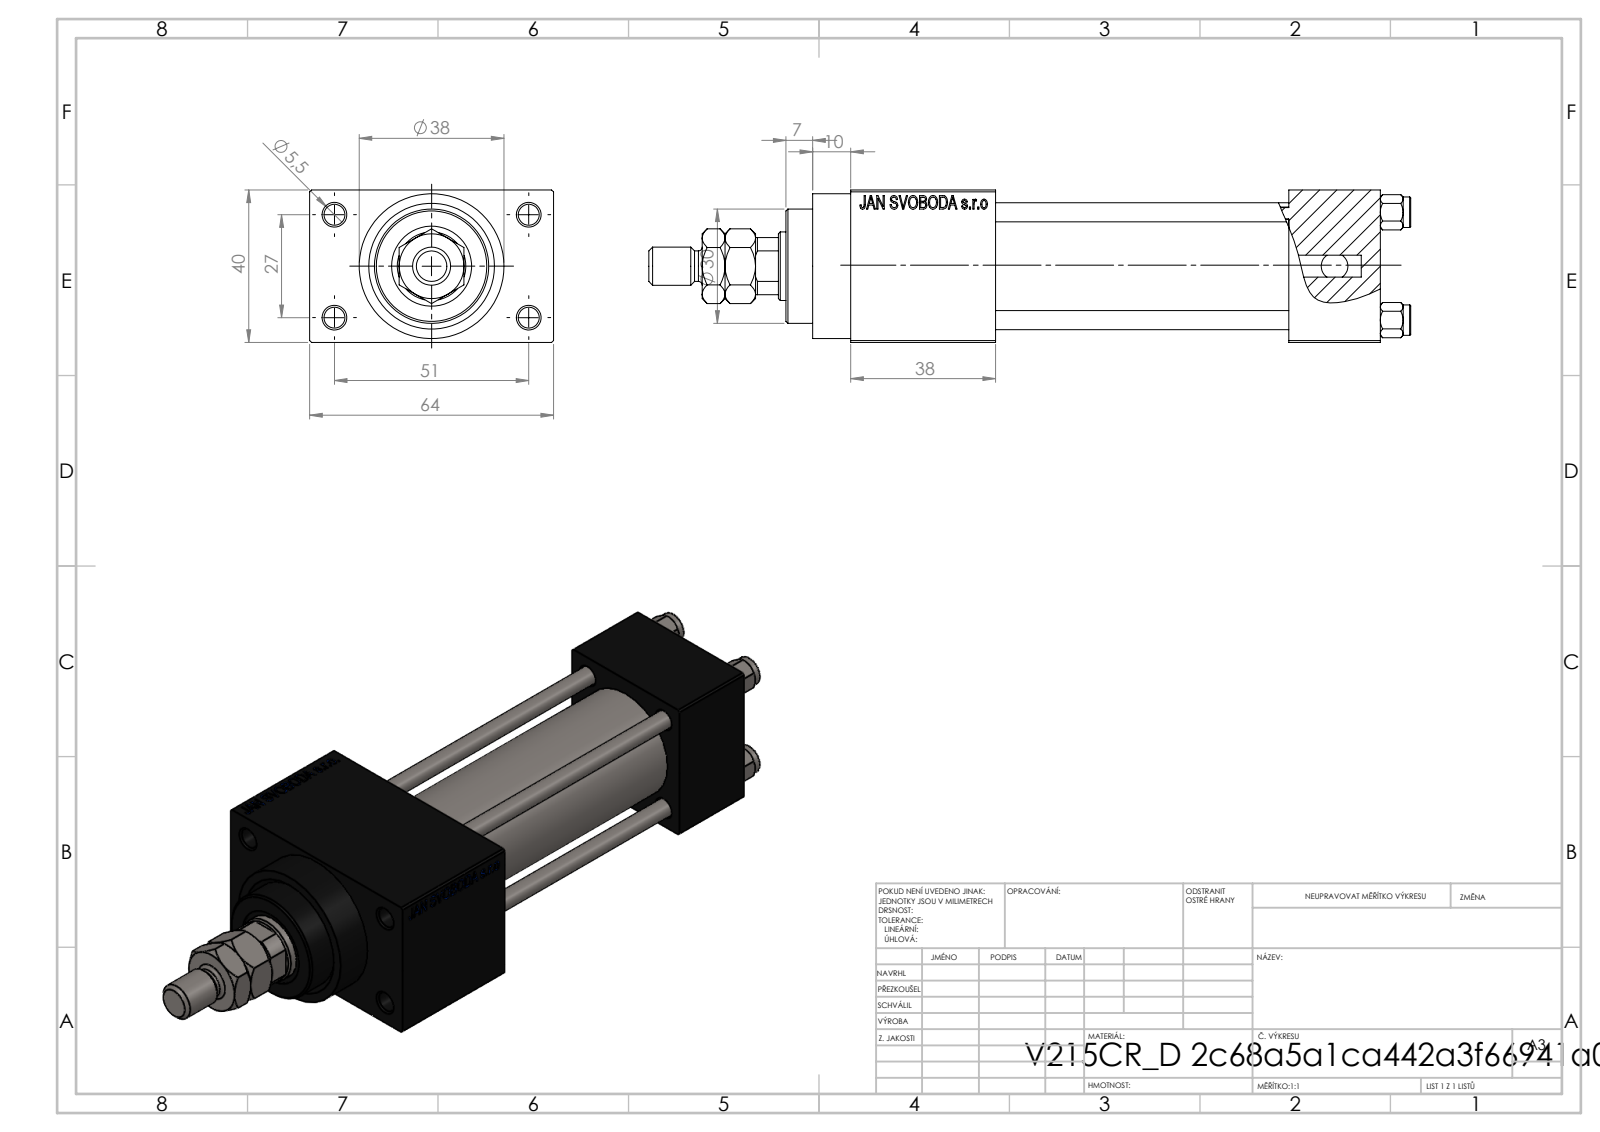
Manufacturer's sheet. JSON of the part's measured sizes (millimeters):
{"part_name": "NUT_M5_D; V215CR_D_TYCINKA; MTA; V215CR_D_Body (+2 more)", "step_written_by": "SolidWorks 2019 (CONFIG_CONTROL_DESIGN)", "units": "millimeters", "bodies": {"solids": 12, "faces": 1150, "planar": 510, "cylindrical": 90, "other": 550}, "overall_size": [200, 64, 40], "volume_mm3": 201516, "surface_area_mm2": 75227, "round_holes": [[5, 4], [5.5, 4], [20, 3], [7, 2], [13.16, 2], [8.5, 1], [18, 1], [21, 1], [25, 1], [30, 1]], "round_bosses_or_shafts": [[8, 5], [38, 1], [31, 1], [10, 1]], "partial_cylinders_radius": [[8.5, 1]], "face_to_face_distances": [40, 77, 12, 24, 101, 52, 38, 139, 115, 64], "hole_center_spacings": [11.37, 20.01, 28.3, 28.85, 29.89, 39.66, 48.34, 27]}
